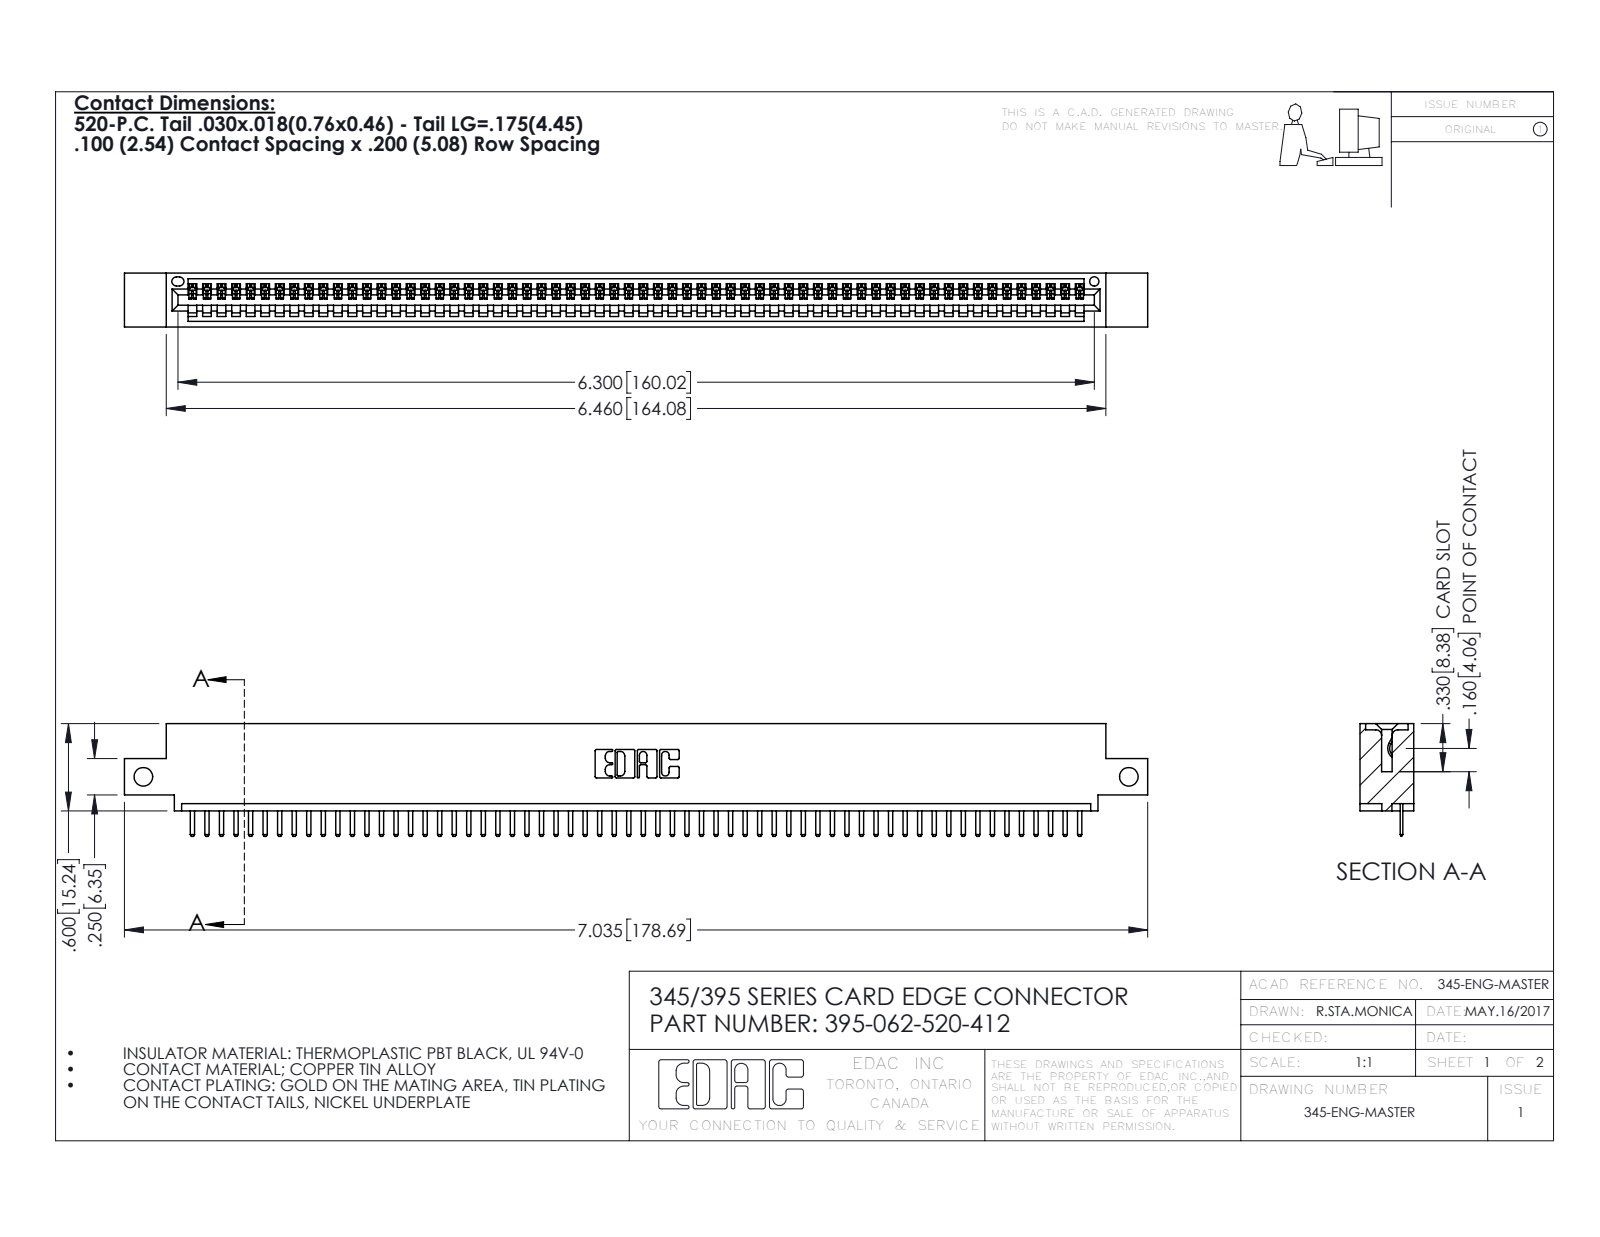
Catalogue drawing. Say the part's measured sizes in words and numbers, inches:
The part is named "395-062-520-412; 345 Part_0.110 Offset - Side Mount; 345-292-001_345-293-120". Its 3-D file was written by "SolidWorks 2016 (CONFIG_CONTROL_DESIGN)". It is 63 solids with 3974 faces: 2688 planar, 1286 cylindrical and 0 other. Overall it measures 7.035 by 0.775 by 0.37 inches. Its volume is 1.025 cubic inches and its surface area 34.02 square inches. Round holes: 2 of diameter 0.128, 1 of diameter 0.064. Partial cylindrical surfaces (rounded edges, fillets, slot ends): 126 of radius 0.01, 124 of radius 0.006, 22 of radius 0.01, 6 of radius 0.007, 6 of radius 0.031, 3 of radius 0.026, 2 of radius 0.031, 2 of radius 0.04. The main face-to-face distances are 0.298, 0.072, 0.37, 0.2, 0.098, 0.272, 0.025, 0.225, 0.072, 0.149. The hole center spacings are 6.775.
